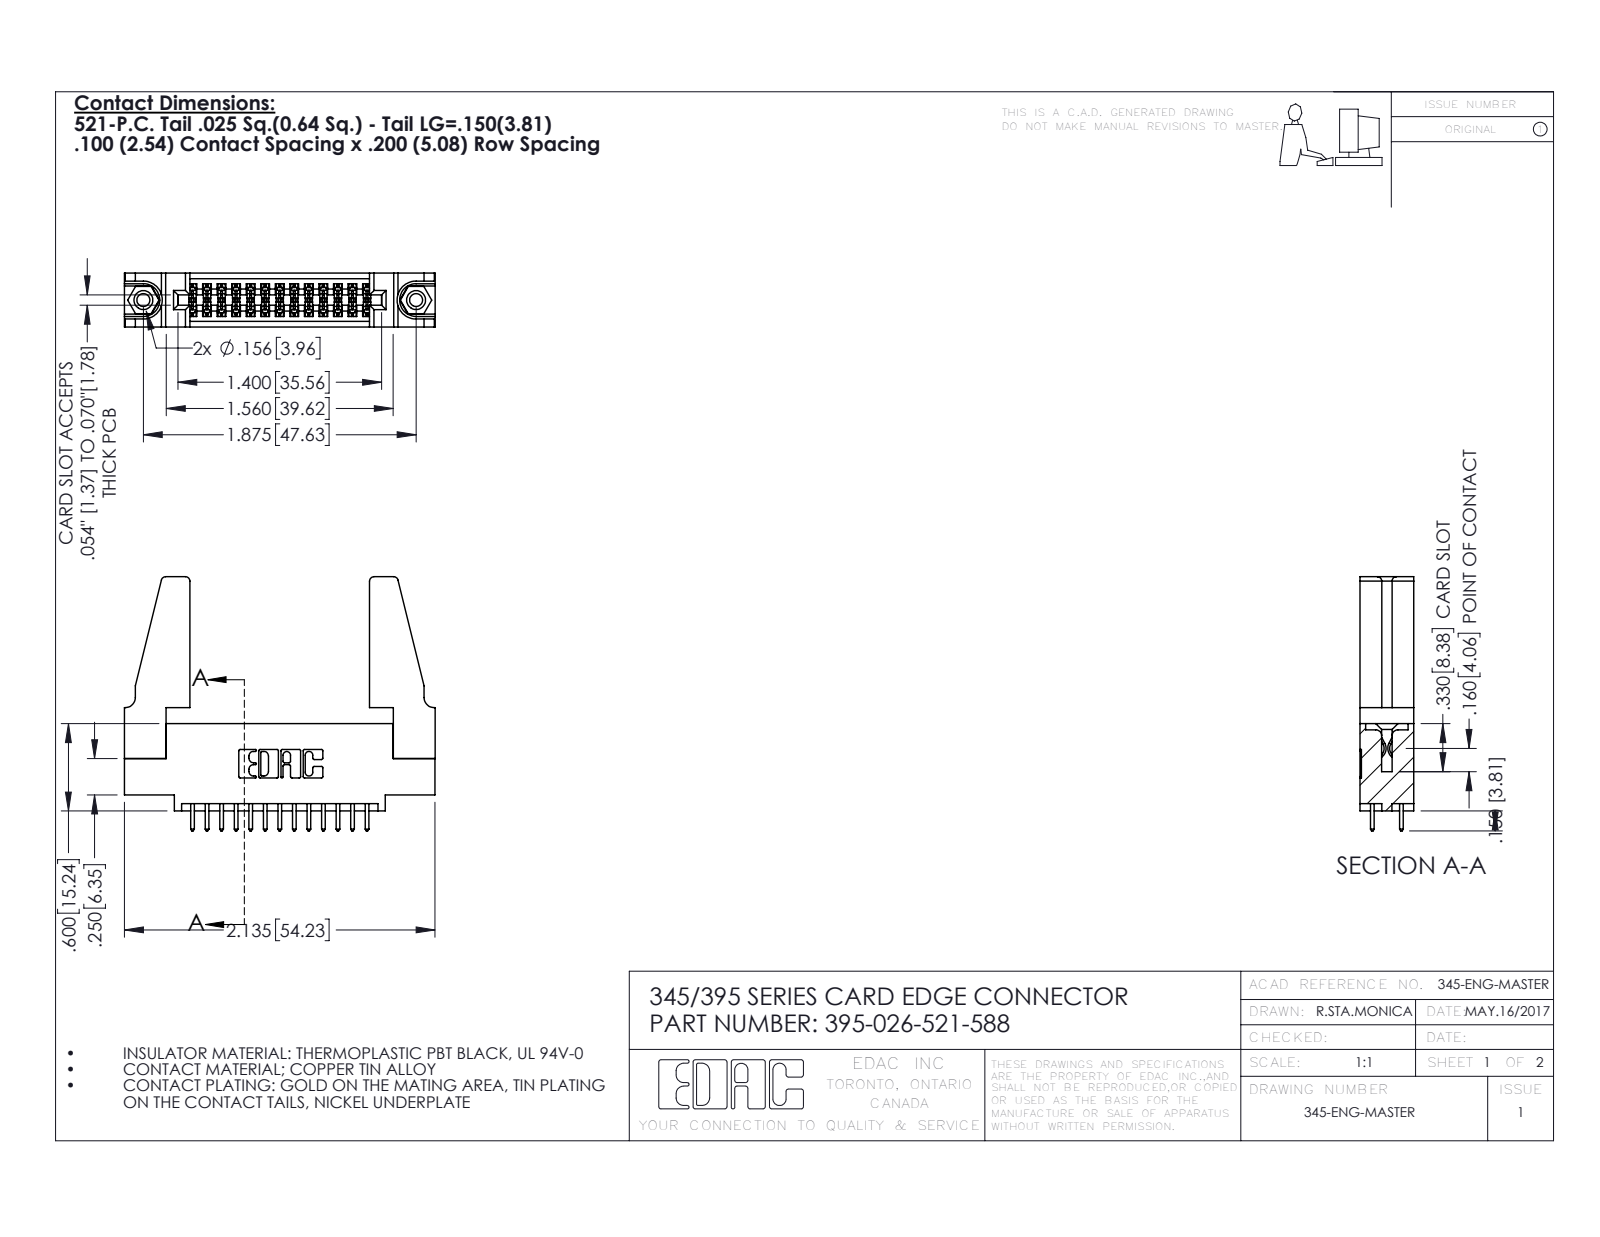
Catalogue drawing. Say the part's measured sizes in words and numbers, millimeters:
The part is named "395-026-521-588; 345-220-078_345-220-088; 345-292-001_345-293-121; 345-250-001_345-250-001-102 (+1 more)". Its 3-D file was written by "SolidWorks 2016 (CONFIG_CONTROL_DESIGN)". It is 31 solids with 1554 faces: 1014 planar, 524 cylindrical and 16 other. Overall it measures 54.3 by 44.4 by 9.4 millimeters. Its volume is 8 180 cubic millimeters and its surface area 9 852 square millimeters. Round holes: 2 of diameter 2.3, 2 of diameter 3.2, 2 of diameter 4, 1 of diameter 1.6. Round bosses or shafts: 2 of diameter 3.9. Partial cylindrical surfaces (rounded edges, fillets, slot ends): 39 of radius 0.2, 26 of radius 0.3, 22 of radius 0.3, 8 of radius 0.8, 6 of radius 0.2, 6 of radius 0.8, 3 of radius 0.7, 2 of radius 0.4. The main face-to-face distances are 9.4, 1.8, 7.6, 5.1, 2.5, 6.9, 0.6, 5.7, 3.8, 3.8. The hole center spacings are 6.9, 41.7, 47.6.
